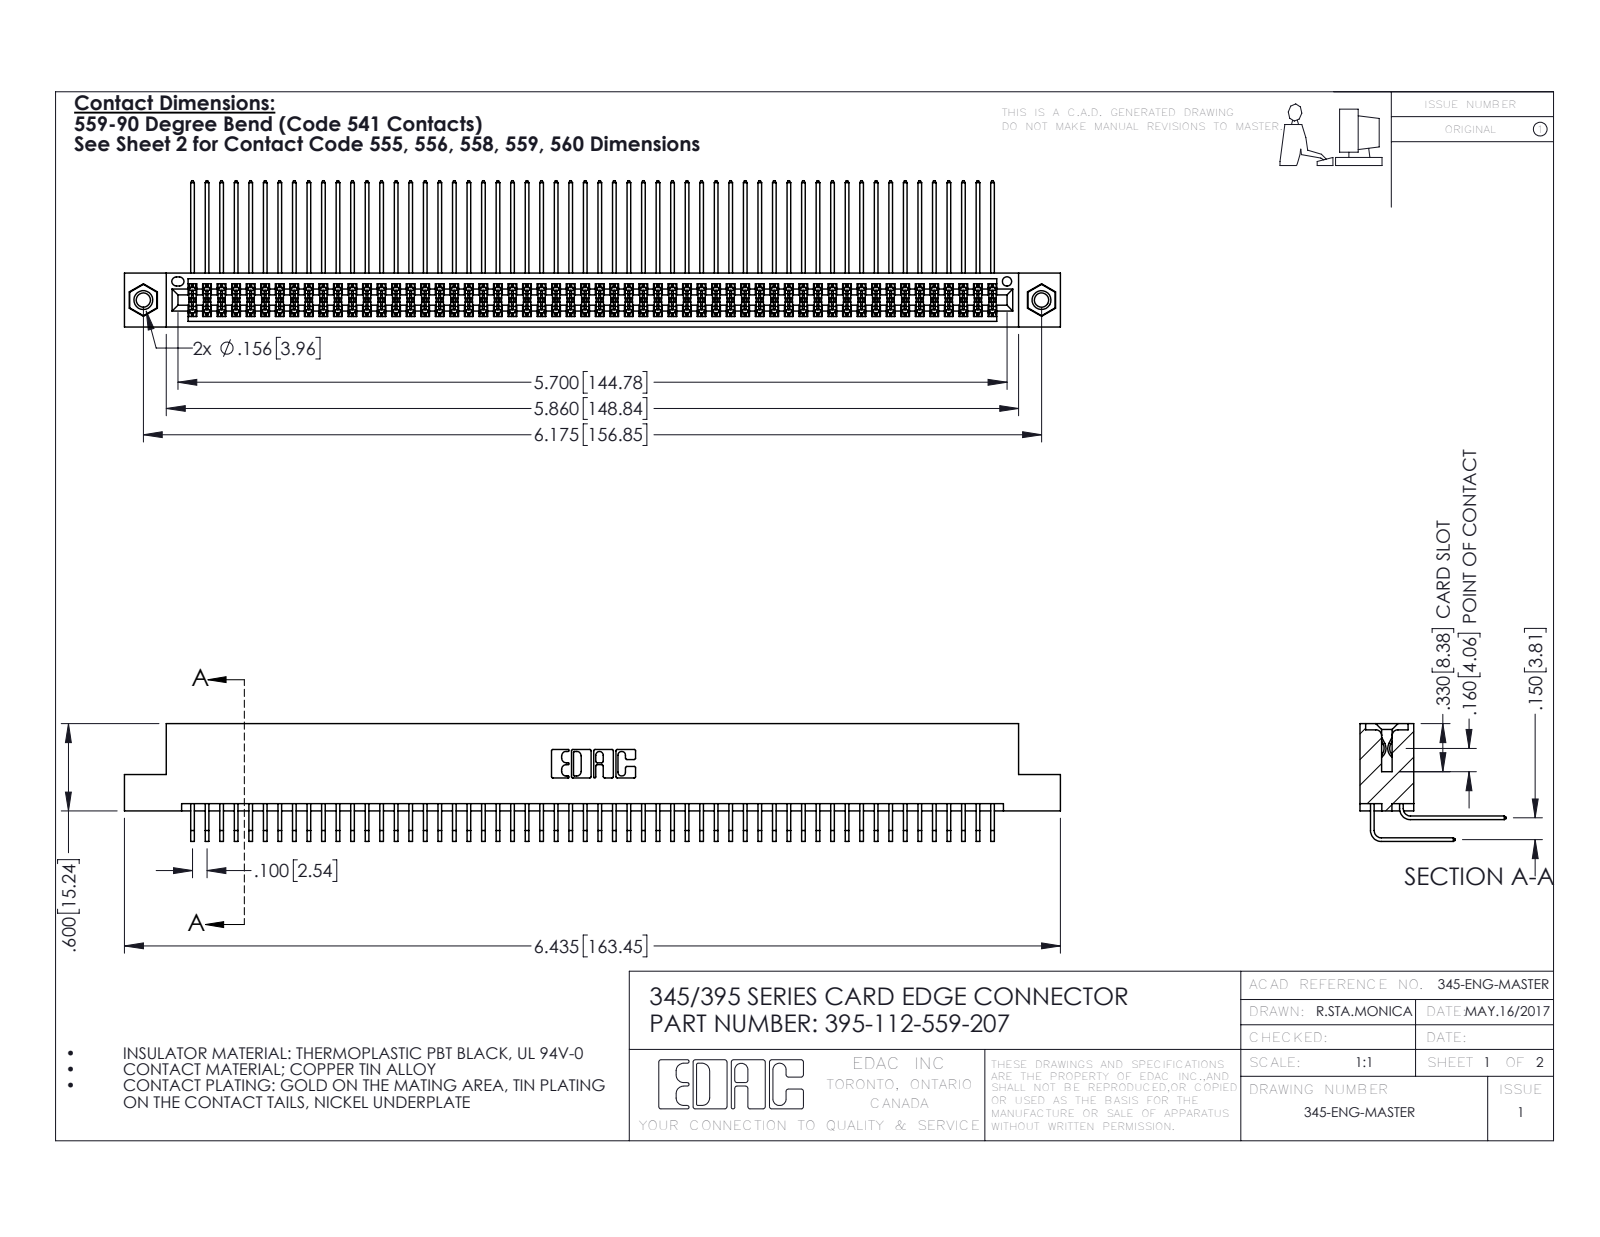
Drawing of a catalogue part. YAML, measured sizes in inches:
part_name: "345-250-001_345-250-005-103; 345-292-001_558 559 Tail - 1; 395-112-559-207; 345 Part_Flush Mounting Lugs - 0.156 Dia-TI (+1 more)"
step_written_by: "SolidWorks 2016 (CONFIG_CONTROL_DESIGN)"
units: inches
bodies: {solids: 115, faces: 6010, planar: 4032, cylindrical: 1962, other: 16}
overall_size: [6.435, 1.005, 0.809]
volume: 1.015
surface_area: 43.3
round_holes:
  - {diameter: 0.098, count: 2}
  - {diameter: 0.125, count: 2}
  - {diameter: 0.156, count: 2}
  - {diameter: 0.064, count: 1}
round_bosses_or_shafts:
  - {diameter: 0.155, count: 2}
partial_cylinders:
  - {radius: 0.006, count: 169}
  - {radius: 0.01, count: 22}
  - {radius: 0.007, count: 6}
  - {radius: 0.031, count: 6}
  - {radius: 0.026, count: 3}
  - {radius: 0.014, count: 2}
  - {radius: 0.019, count: 2}
  - {radius: 0.022, count: 2}
face_to_face_distances: [0.072, 0.298, 0.2, 0.37, 0.098, 0.272, 0.025, 0.225, 0.175, 0.15]
hole_center_spacings: [0.27, 5.939, 6.175]
